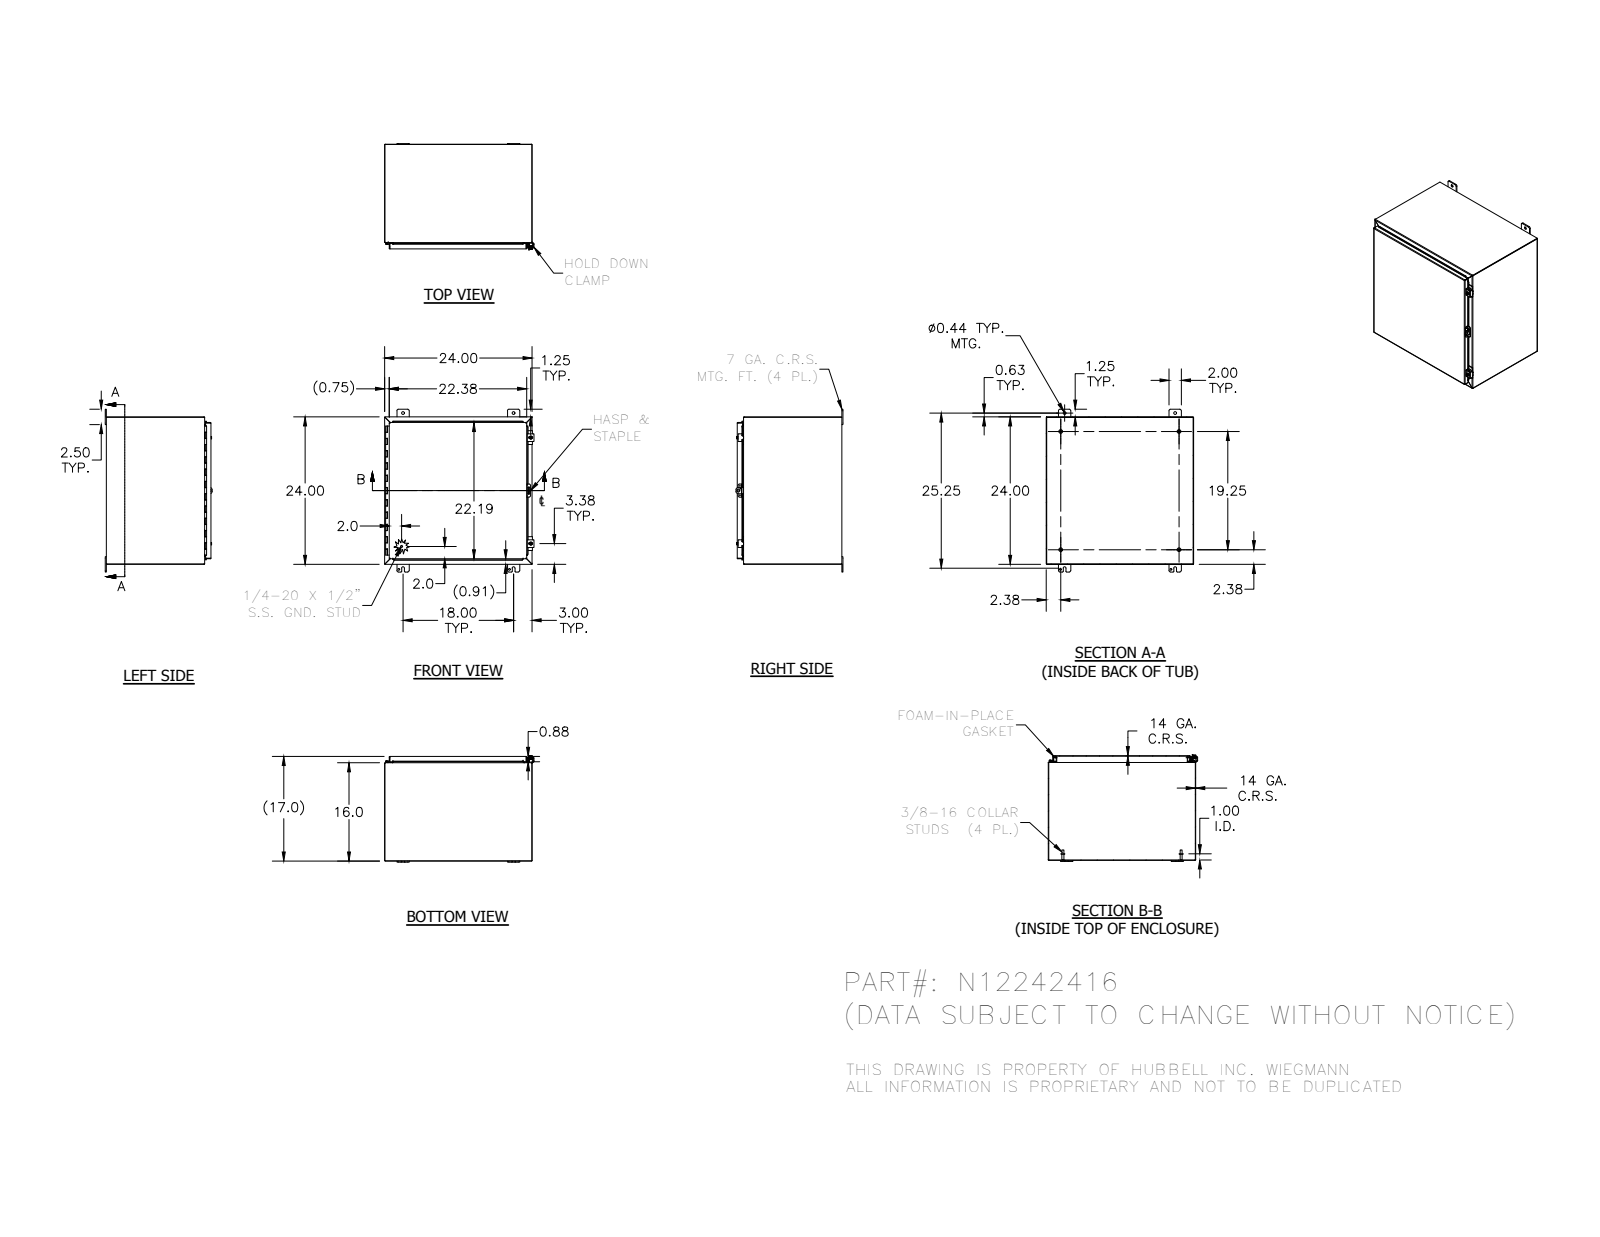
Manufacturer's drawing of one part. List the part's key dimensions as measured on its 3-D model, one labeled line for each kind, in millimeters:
Part name (STEP PRODUCT): N12242416; 34840; 38413; N122416TB (+8 more)
STEP written by: Autodesk Inventor 2012 (AUTOMOTIVE_DESIGN)
Units: millimetres
Bodies: 29 solids, 870 faces (507 planar, 262 cylindrical, 101 other)
Overall size (bounding box): 673.1 × 617.5 × 442.2
Volume: 3 767 000 mm³ · Surface area: 3 916 000 mm²
Round holes (diameter × count): ⌀8 ×4, ⌀11.1 ×4, ⌀2.8 ×3, ⌀5.4 ×2, ⌀7.1 ×2, ⌀7.6 ×2, ⌀3.2 ×1, ⌀4 ×1, ⌀12.7 ×1
Round bosses / shafts (diameter × count): ⌀15.9 ×4, ⌀8.4 ×4, ⌀6.4 ×4, ⌀13.2 ×2, ⌀12.7 ×2, ⌀8.9 ×2, ⌀2.9 ×2, ⌀8.6 ×1
Partial cylindrical surfaces — rounded edges, fillets, slot ends (radius × count): R0.8 ×27, R3.2 ×25, R6.4 ×25, R0.8 ×21, R2.7 ×21, R1.6 ×13, R2.5 ×4, R3.6 ×4
Main face-to-face distances: 1.9, 607.7, 430.8, 605.8, 609.6, 428.9, 432.6, 404.5, 26.2, 406.4
Hole centre spacings: 40.5, 457.2, 609.6, 762, 20.1, 441.2, 476, 573.4
